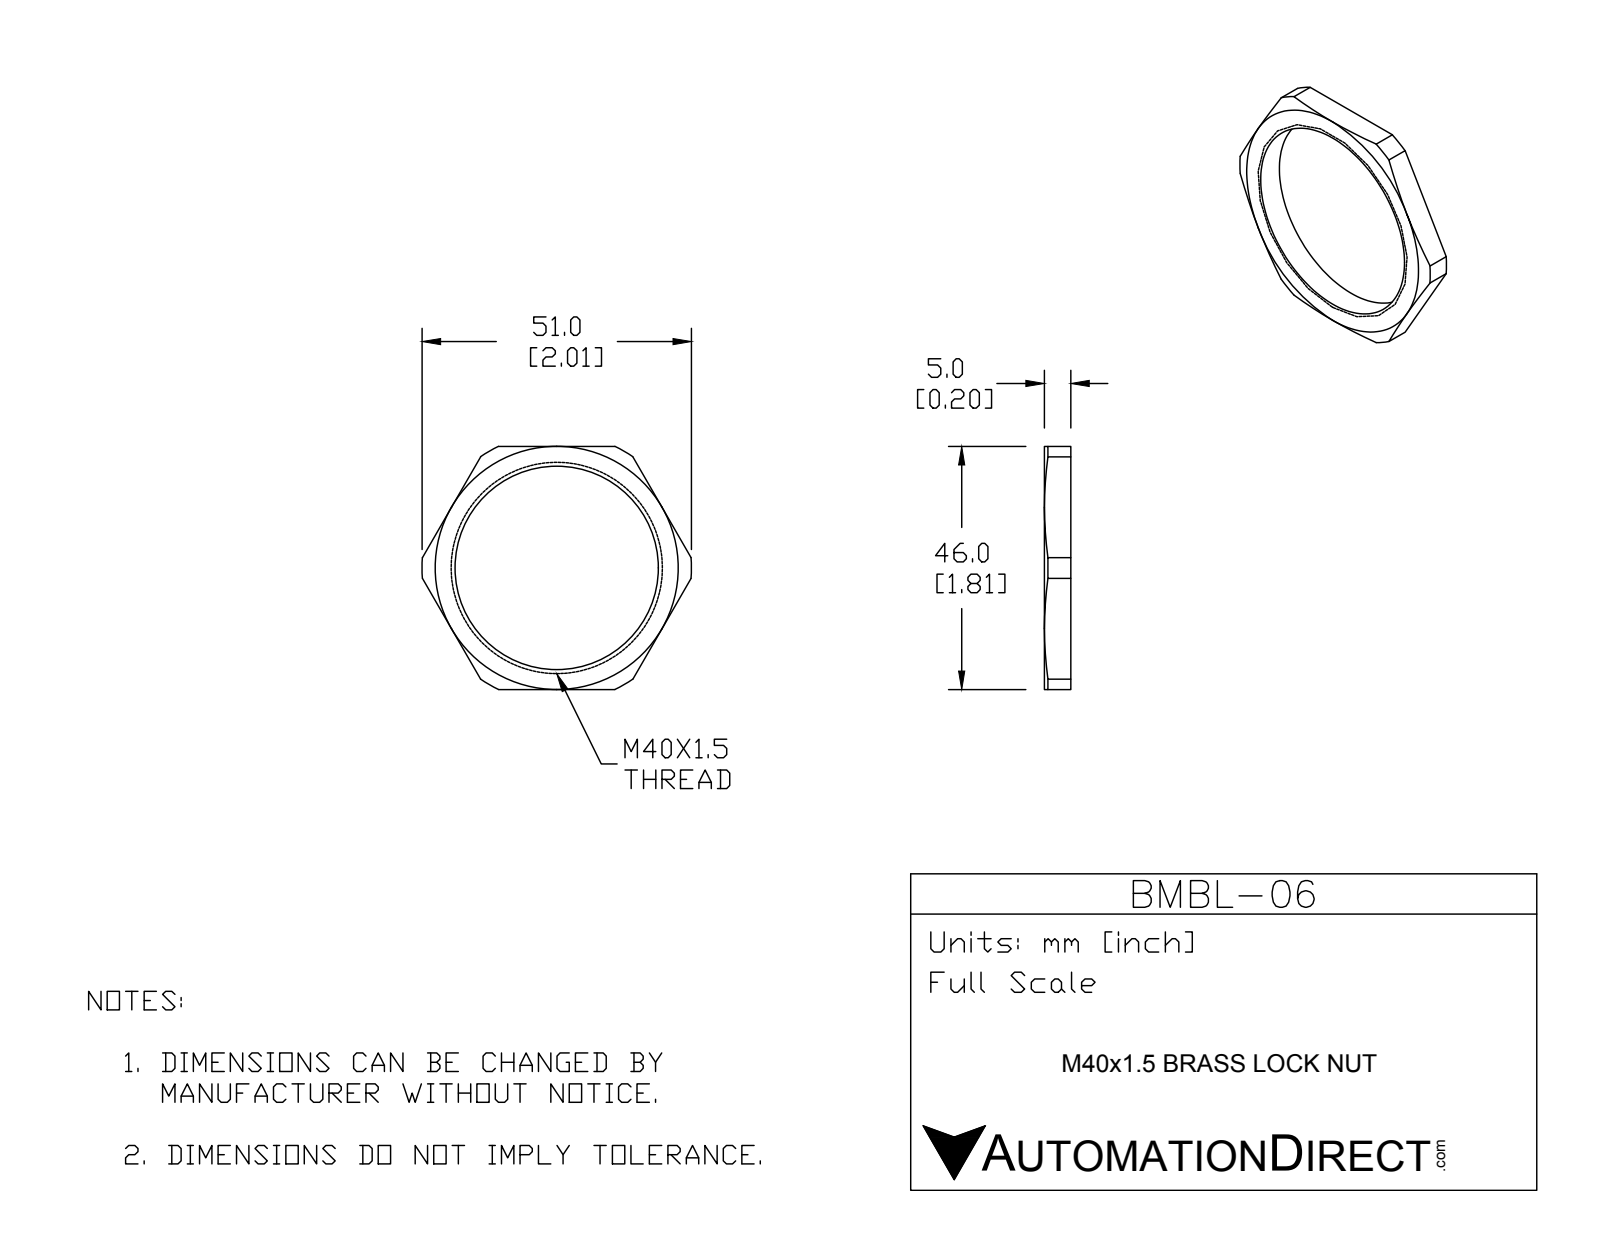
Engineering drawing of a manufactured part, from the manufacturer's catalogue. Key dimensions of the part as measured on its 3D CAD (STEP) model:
Part name (STEP PRODUCT): BMBL-06
STEP written by: SolidWorks 2015 (CONFIG_CONTROL_DESIGN)
Units: millimetres
Bodies: 1 solid, 23 faces (8 planar, 9 cylindrical, 6 other)
Overall size (bounding box): 51 × 46 × 5
Volume: 3 241 mm³ · Surface area: 2 655 mm²
Round holes (diameter × count): ⌀38.5 ×1
Partial cylindrical surfaces — rounded edges, fillets, slot ends (radius × count): R25.5 ×1
Main face-to-face distances: 5, 46
